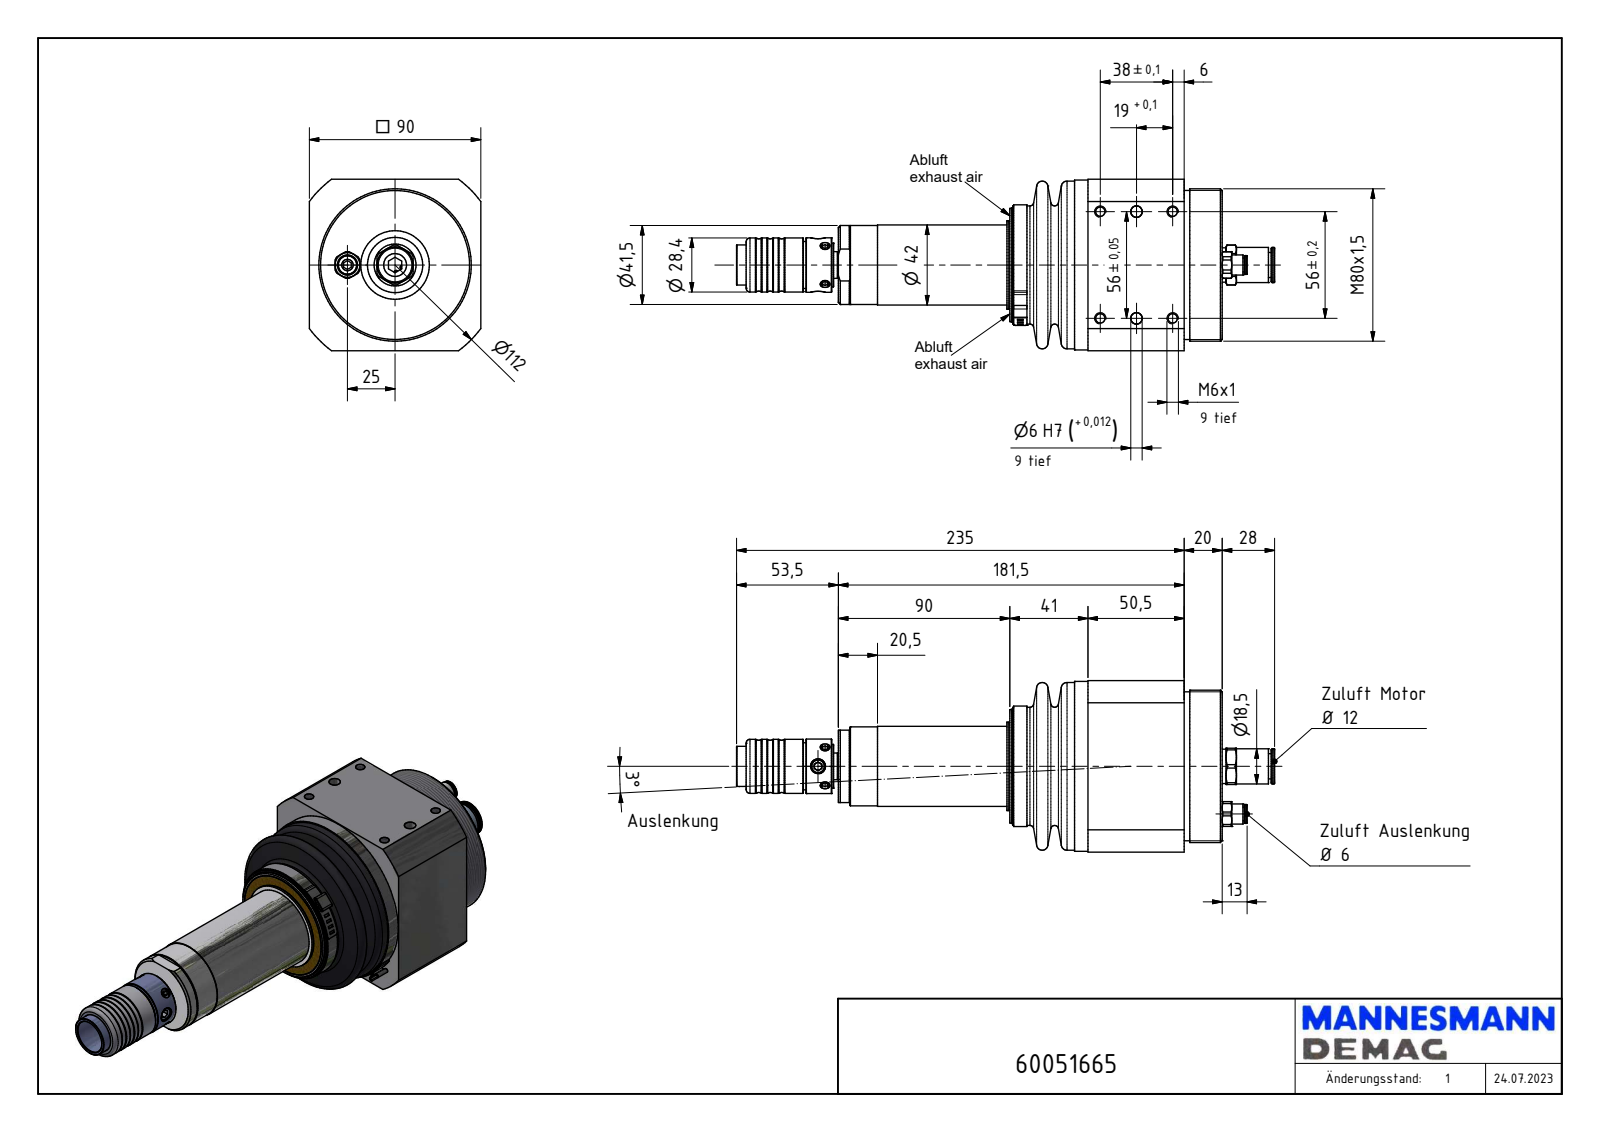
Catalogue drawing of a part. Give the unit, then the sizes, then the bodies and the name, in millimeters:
Units: millimetres
Overall size (bounding box): 282.55 × 90 × 90
Round holes (diameter × count): ⌀6 ×15, ⌀4.92 ×4, ⌀2.5 ×2, ⌀3.5 ×2, ⌀4 ×2, ⌀4.13 ×2, ⌀5 ×2, ⌀5.6 ×1, ⌀6.1 ×1, ⌀6.19 ×1, ⌀6.65 ×1, ⌀8.05 ×1
Round bosses / shafts (diameter × count): ⌀5 ×2, ⌀89.2 ×1, ⌀86 ×1, ⌀85.5 ×1, ⌀85.44 ×1, ⌀78.16 ×1, ⌀78 ×1, ⌀73.84 ×1
Partial cylindrical surfaces — rounded edges, fillets, slot ends (radius × count): R4.65 ×98, R0.5 ×8, R1 ×8, R1.1 ×8, R10 ×6, R1.4 ×4, R2 ×4, R2.5 ×2
Main face-to-face distances: 90, 54, 10, 58.09, 3.5, 70.5, 12.41, 16.5, 20, 4
Hole centre spacings: 15, 7.76, 21.21, 25.98, 28.98, 30, 8.59, 13.05
Volume: 994 147 mm³ · Surface area: 254 062 mm²
Bodies: 28 solids, 917 faces (298 planar, 442 cylindrical, 177 other)
Part name (STEP PRODUCT): ESR 20 WS_60051665
STEP written by: Autodesk Inventor 2014 (AUTOMOTIVE_DESIGN)
